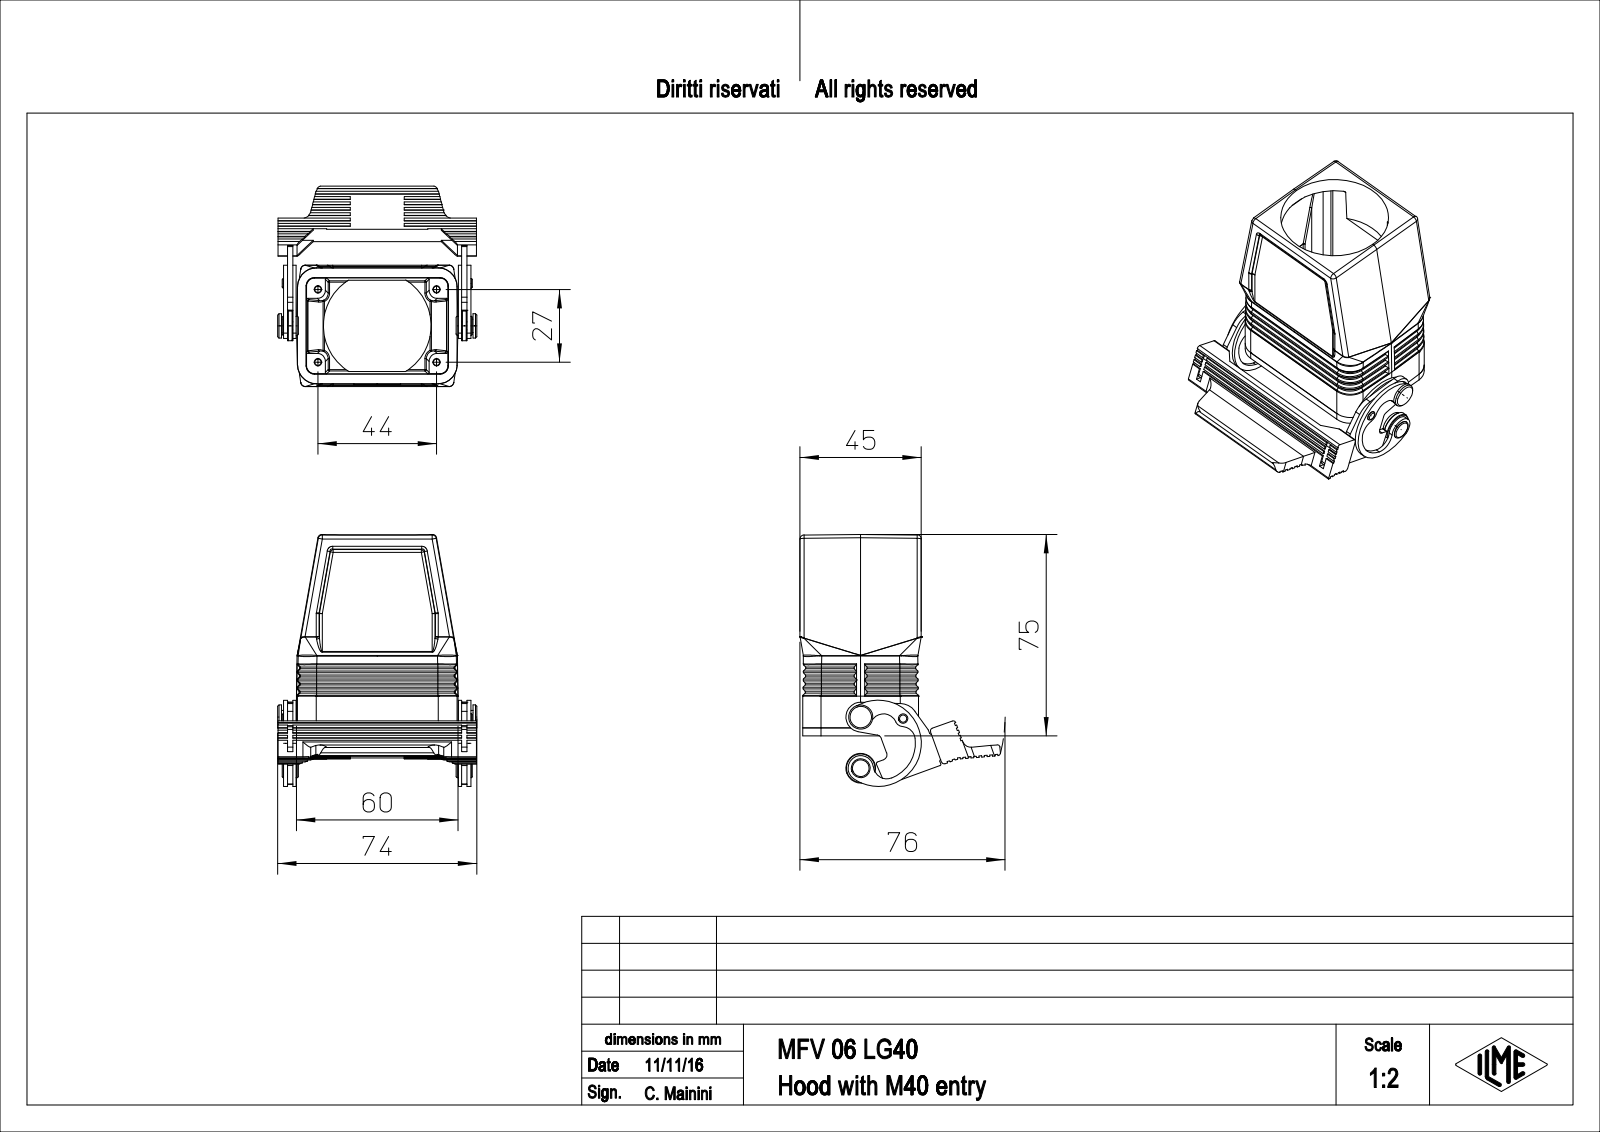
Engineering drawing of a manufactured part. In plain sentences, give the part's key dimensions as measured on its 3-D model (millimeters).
The part is named "MFV_06_LG40". Its 3-D file was written by "PTC Creo Elements/Direct Modeling 19.0E 27-Jun-2016 (C) Parametric Technology GmbH (AUTOMOTIVE_DESIGN)". It is 1 solid with 766 faces: 386 planar, 236 cylindrical and 144 other. Overall it measures 93.5 by 74.37 by 73.9 millimeters. Its volume is 69 051 cubic millimeters and its surface area 40 295 square millimeters. Round holes: 4 of diameter 2.75, 1 of diameter 3.1, 1 of diameter 4, 1 of diameter 5, 1 of diameter 40. Round bosses or shafts: 1 of diameter 11, 1 of diameter 9, 1 of diameter 7, 1 of diameter 5, 1 of diameter 3.5, 1 of diameter 3. Partial cylindrical surfaces (rounded edges, fillets, slot ends): 58 of radius 0.5, 16 of radius 3, 13 of radius 1.5, 9 of radius 7, 5 of radius 1, 4 of radius 4.2, 4 of radius 5.8, 3 of radius 5. The main face-to-face distances are 2, 43, 3.5, 64.6, 4, 7, 1, 1.5, 68.1, 3. The hole center spacings are 25.81, 27, 44, 51.62, 19.12, 24.25, 34.07.
